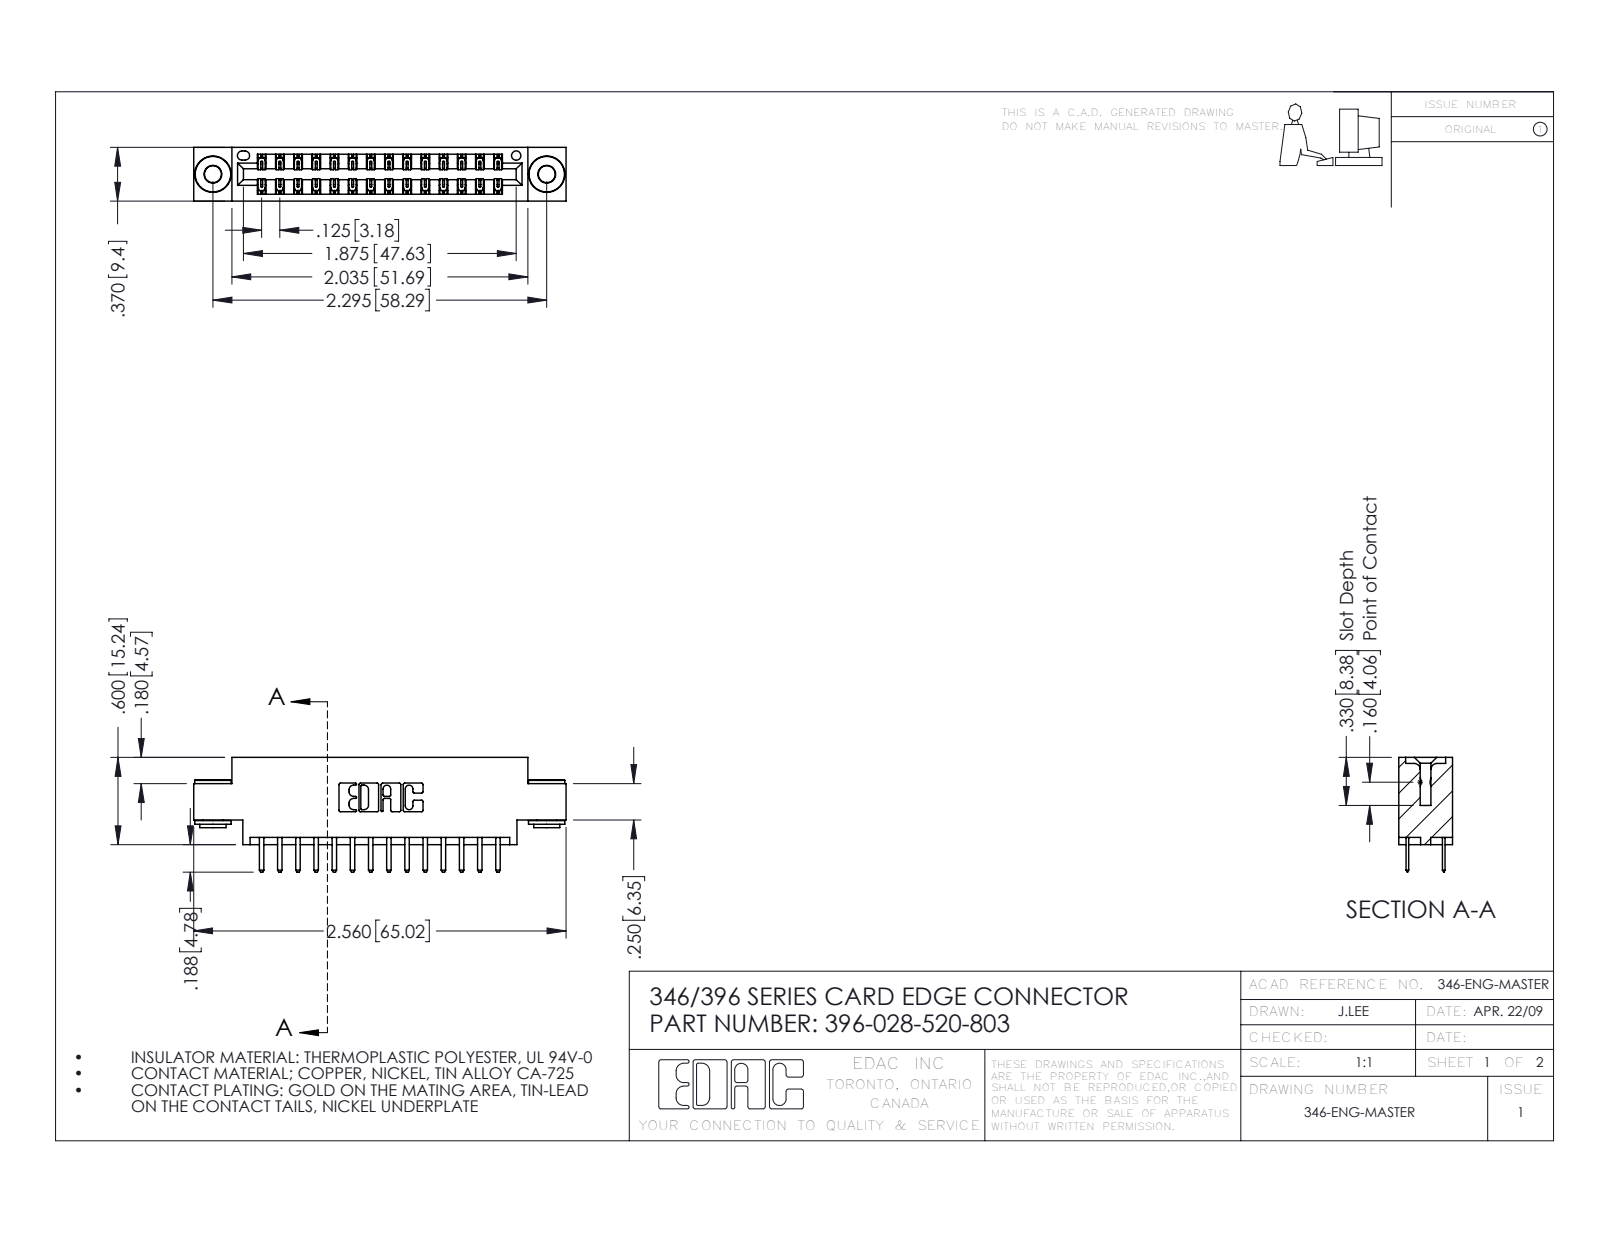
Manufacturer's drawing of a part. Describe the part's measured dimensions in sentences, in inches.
The part is named "345-250-002_345-250-002-102; 396-028-520-803; 345-292-001_345-293-120; 346 Part_0.170 Offset - 0.156 Dia-TH". Its 3-D file was written by "SolidWorks 2016 (CONFIG_CONTROL_DESIGN)". It is 31 solids with 1732 faces: 1126 planar, 598 cylindrical and 8 other. Overall it measures 2.56 by 0.788 by 0.37 inches. Its volume is 0.365 cubic inches and its surface area 12.62 square inches. Round holes: 2 of diameter 0.116, 2 of diameter 0.156, 1 of diameter 0.064. Round bosses or shafts: 2 of diameter 0.25, 2 of diameter 0.18, 2 of diameter 0.136. Partial cylindrical surfaces (rounded edges, fillets, slot ends): 42 of radius 0.006, 32 of radius 0.01, 22 of radius 0.01, 6 of radius 0.007, 6 of radius 0.031, 3 of radius 0.026, 2 of radius 0.014, 2 of radius 0.022. The main face-to-face distances are 0.25, 0.37, 0.048, 0.322, 0.025, 0.275, 0.072, 0.298, 0.148, 0.222. The hole center spacings are 0.246, 2.089, 2.295.
